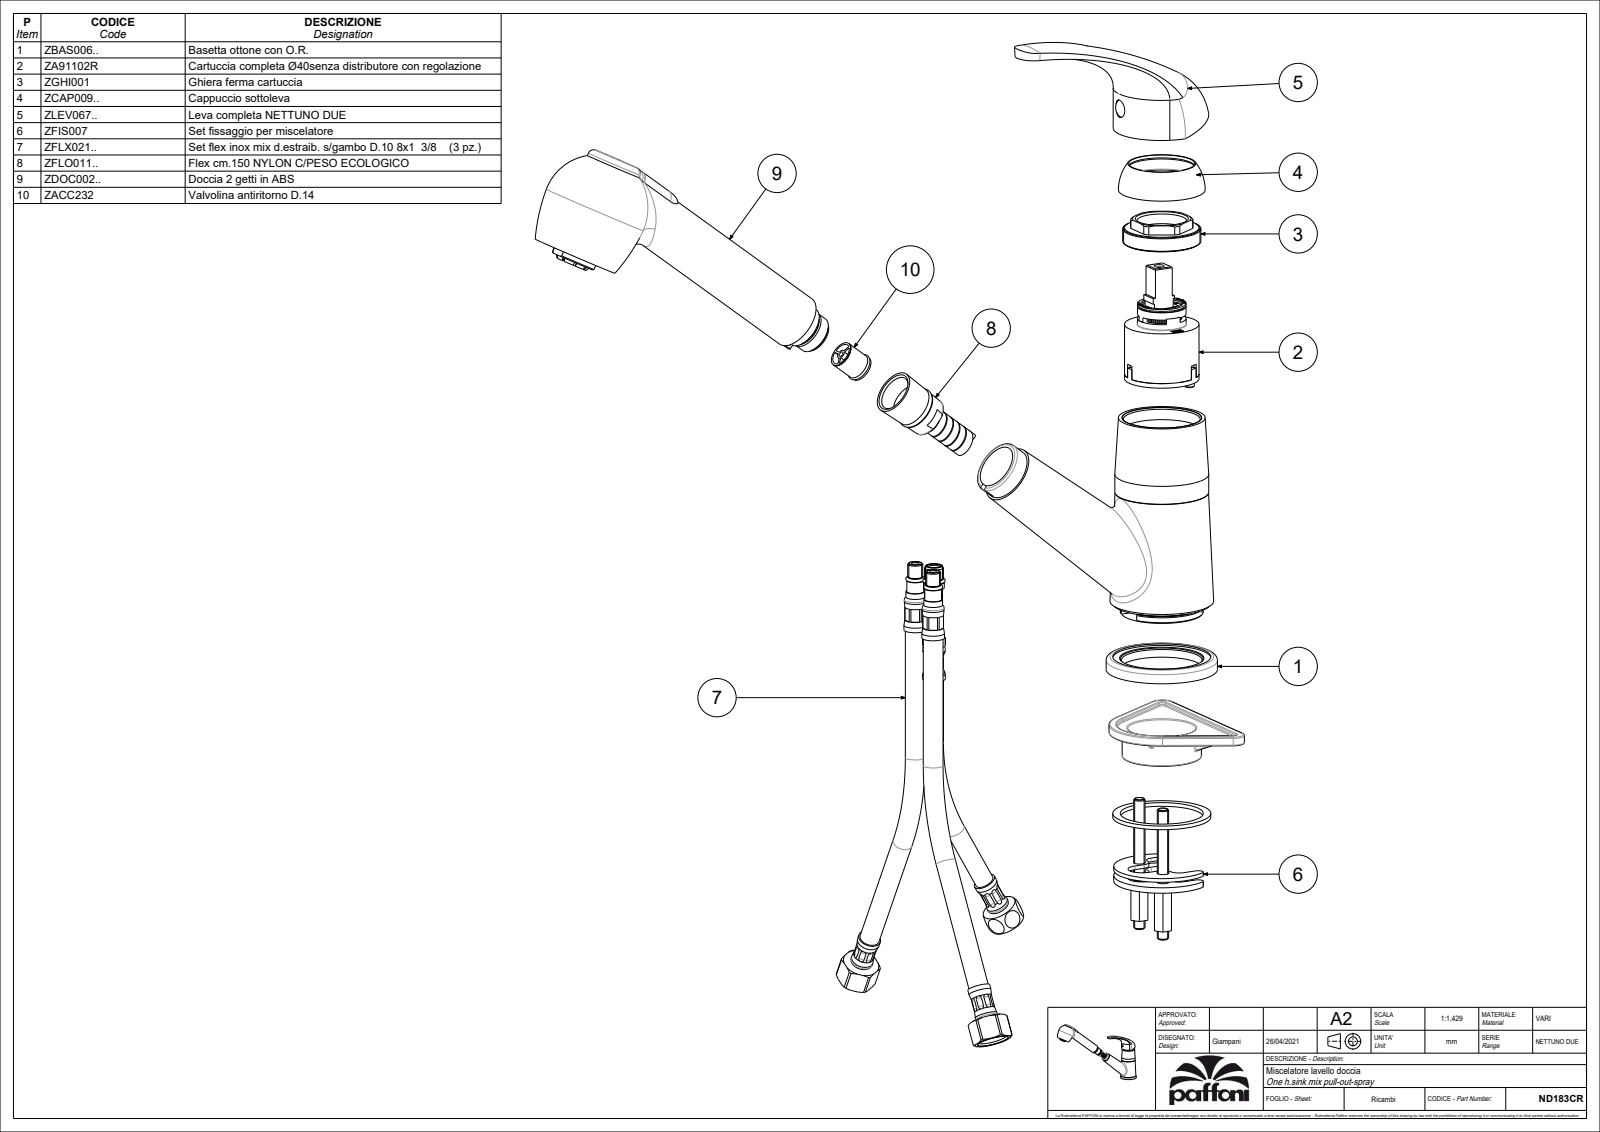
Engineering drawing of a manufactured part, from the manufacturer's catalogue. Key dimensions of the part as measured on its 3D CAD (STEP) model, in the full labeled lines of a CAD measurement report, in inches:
Part name (STEP PRODUCT): ND183CR
STEP written by: CREO PARAMETRIC BY PTC INC, 2020044 (CONFIG_CONTROL_DESIGN)
Units: inches
Bodies: 3 solids, 278 faces (103 planar, 67 cylindrical, 108 other)
Overall size (bounding box): 11.268 × 8.046 × 2.323
Volume: 20.86 in³ · Surface area: 166.4 in²
Round holes (diameter × count): ⌀0.236 ×1, ⌀0.63 ×1, ⌀1.031 ×1, ⌀1.378 ×1, ⌀1.594 ×1, ⌀1.602 ×1, ⌀1.61 ×1, ⌀1.681 ×1, ⌀1.732 ×1, ⌀1.744 ×1, ⌀1.898 ×1, ⌀1.949 ×1
Round bosses / shafts (diameter × count): ⌀0.197 ×2, ⌀2.323 ×1, ⌀1.961 ×1, ⌀1.764 ×1, ⌀1.161 ×1, ⌀1.122 ×1, ⌀1.024 ×1, ⌀0.906 ×1
Partial cylindrical surfaces — rounded edges, fillets, slot ends (radius × count): R0.315 ×2, R0.079 ×1, R0.154 ×1, R0.157 ×1, R0.472 ×1, R0.591 ×1, R1.969 ×1
Main face-to-face distances: 4.826, 0.039, 4.824, 4.827, 2.642, 0.038, 4.786, 4.787, 0.244, 0.243
